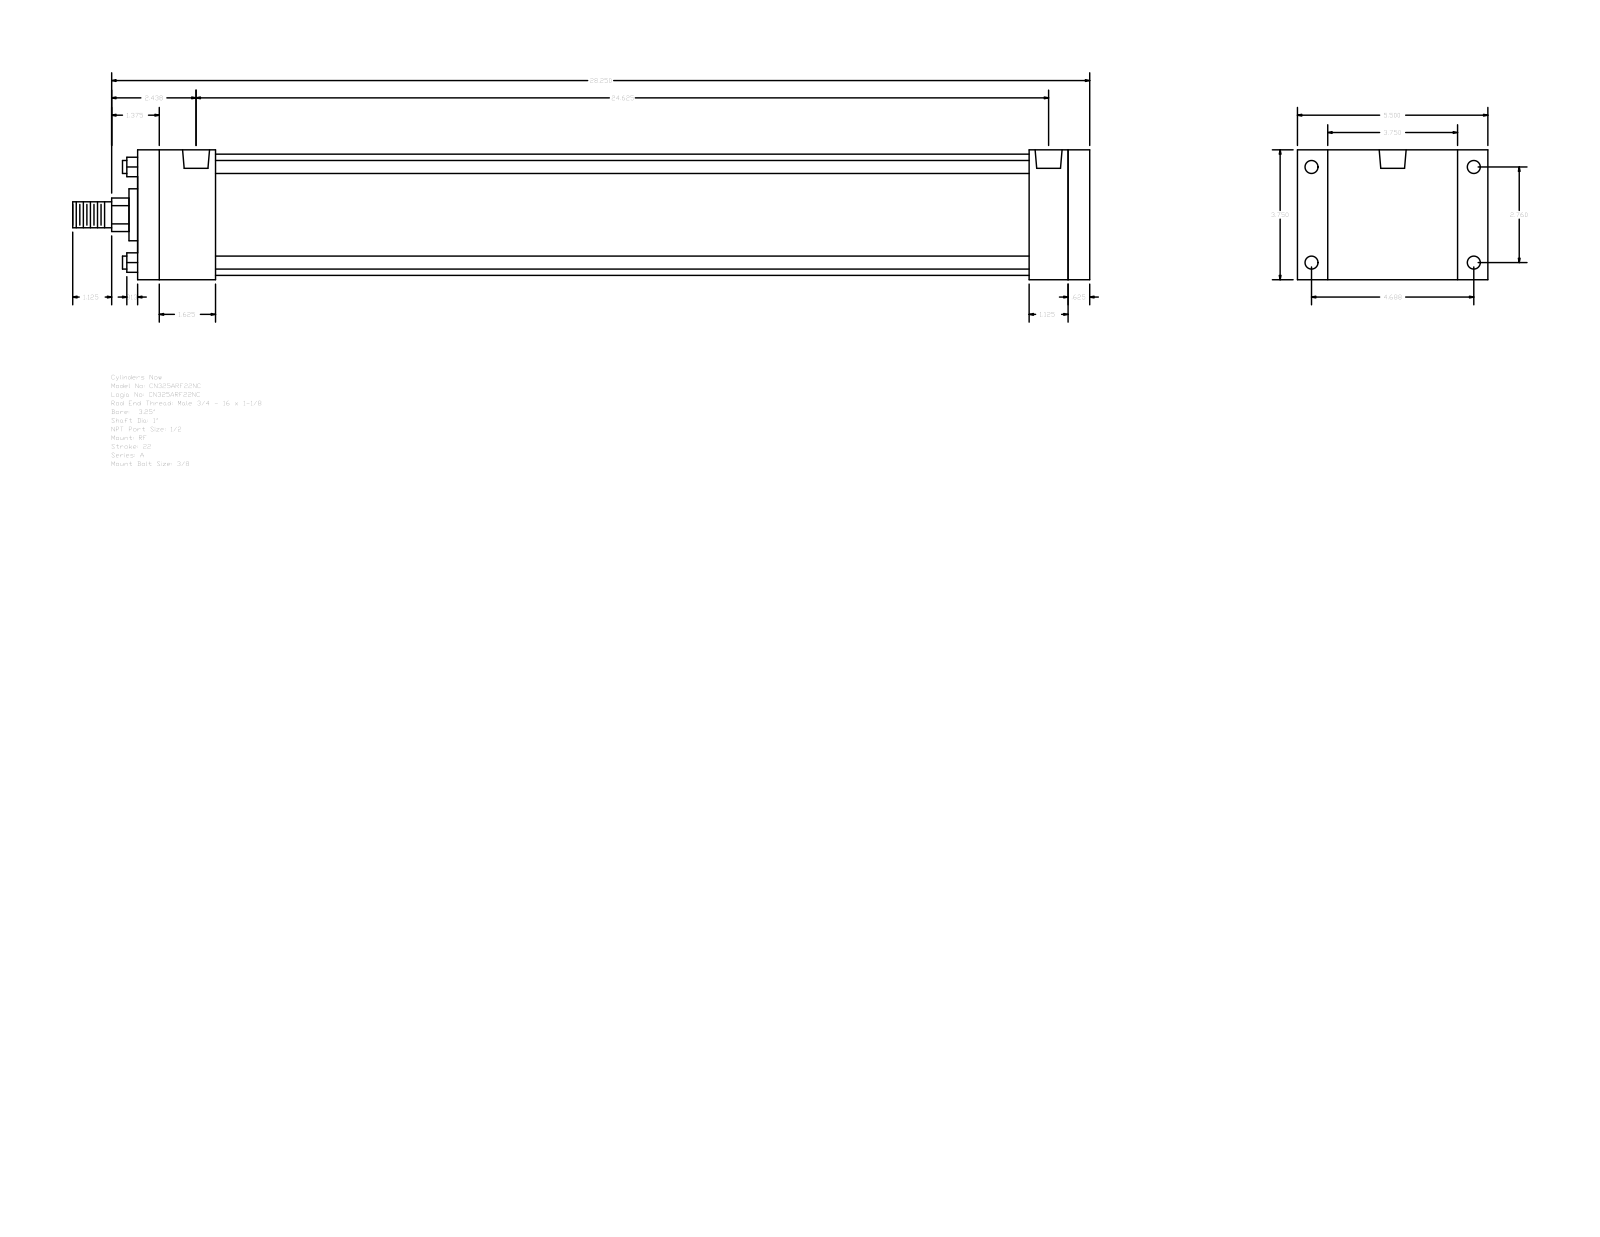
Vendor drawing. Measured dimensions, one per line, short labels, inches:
name: A_RF__0325_1
written by: GSSL Pune (CONFIG_CONTROL_DESIGN)
unit: in
bodies: 0 solids, 92 faces (64 planar, 28 cylindrical, 0 other)
size: 29.375 × 5.5 × 3.75
holes: 4× ⌀0.344, 4× ⌀0.375, 2× ⌀0.778
bosses: 4× ⌀0.375, 1× ⌀3.5, 1× ⌀1.5, 1× ⌀1, 1× ⌀0.75
rounds: 1× R0.484
face distances: 3.75, 27.5, 26.875, 0.625, 0.875, 4.625, 1.125, 25.75, 1.75, 2.25
hole spacings: 0.125, 2.76, 4.687, 5.439, 24.375, 24.5, 24.625
